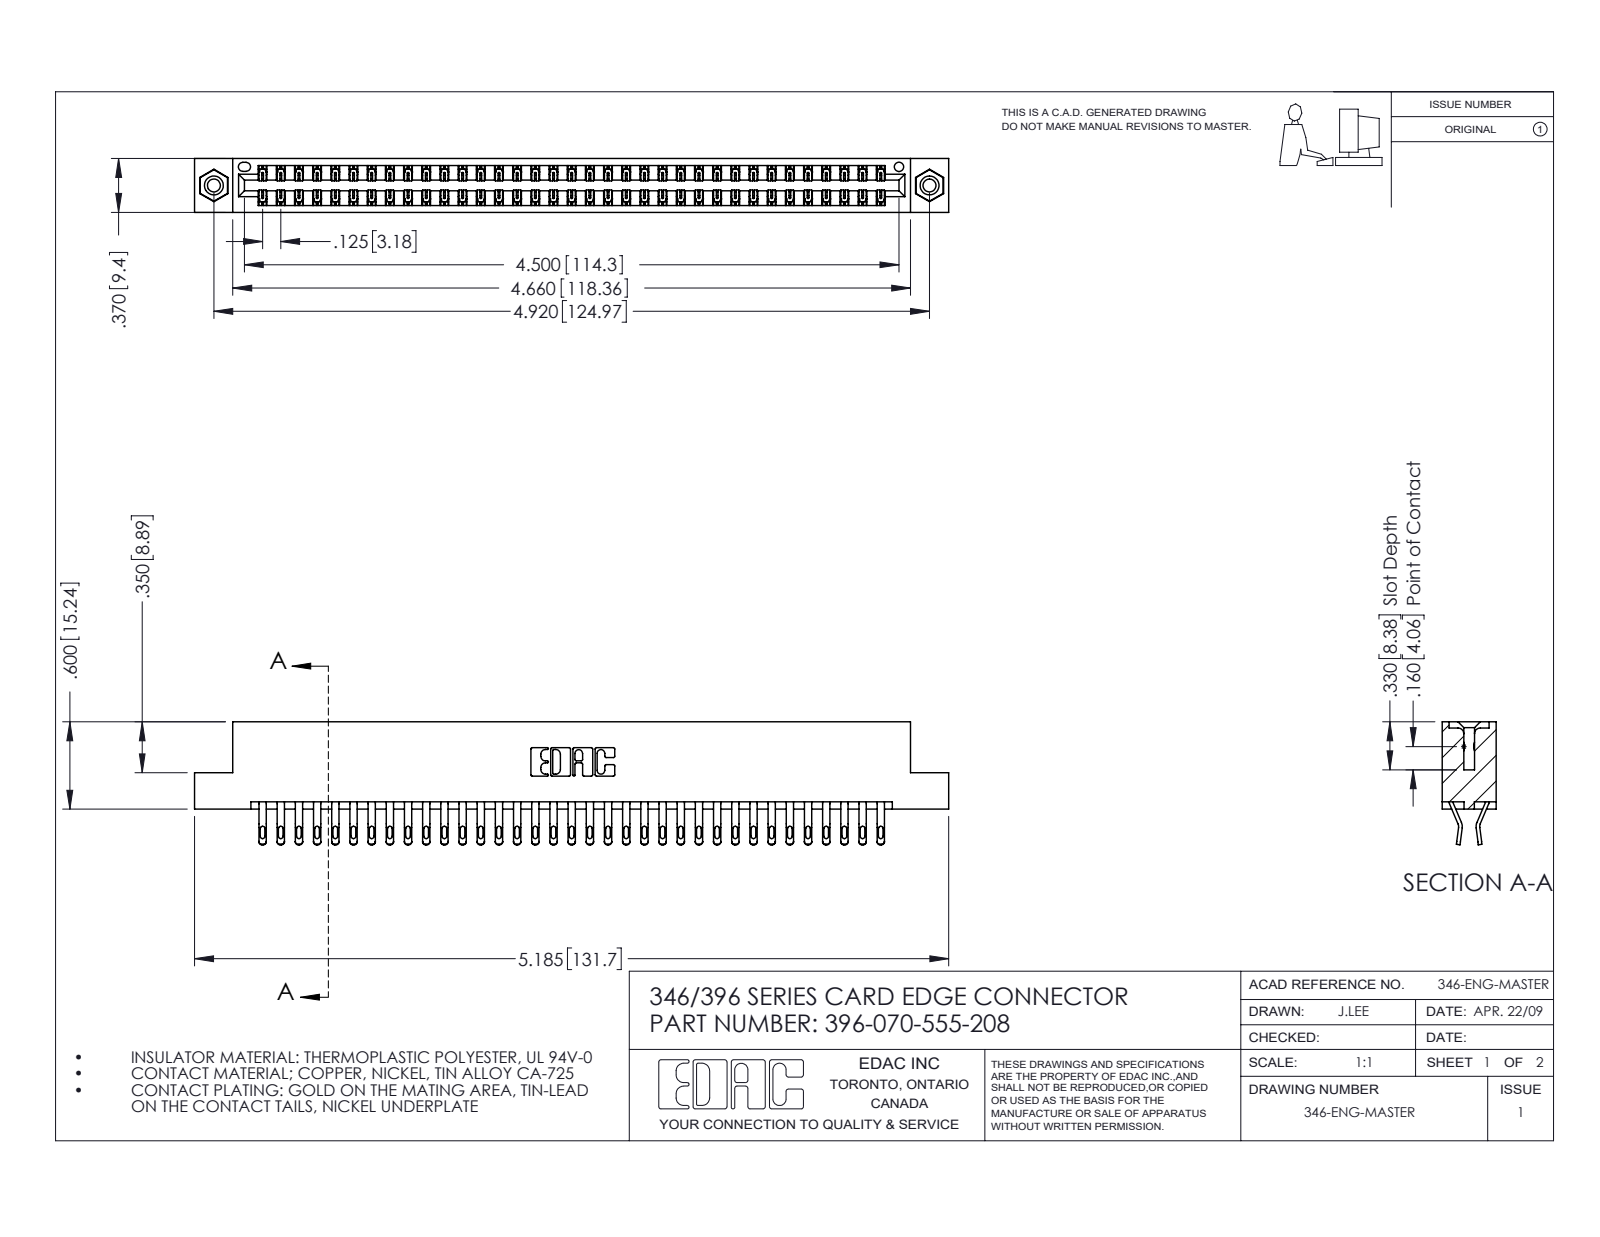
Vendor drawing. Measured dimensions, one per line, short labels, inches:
name: 345-250-001_345-250-003-102; 396-070-555-208; 345-292-001_555 Tail; 346 Part_Flush Mounting Lugs - 0.156 Dia-TI
written by: SolidWorks 2016 (CONFIG_CONTROL_DESIGN)
unit: in
bodies: 73 solids, 4242 faces (2418 planar, 1808 cylindrical, 16 other)
size: 5.185 × 0.845 × 0.37
volume: 0.792 in³; area: 28.65 in²
holes: 2× ⌀0.089, 2× ⌀0.125, 2× ⌀0.156, 1× ⌀0.064
bosses: 2× ⌀0.155
rounds: 140× R0.016, 140× R0.02, 105× R0.006, 22× R0.01, 6× R0.007, 6× R0.031, 3× R0.026, 2× R0.01
face distances: 0.048, 0.322, 0.37, 0.25, 0.025, 0.072, 0.298, 0.275, 0.148, 0.222
hole spacings: 0.246, 4.711, 4.92
